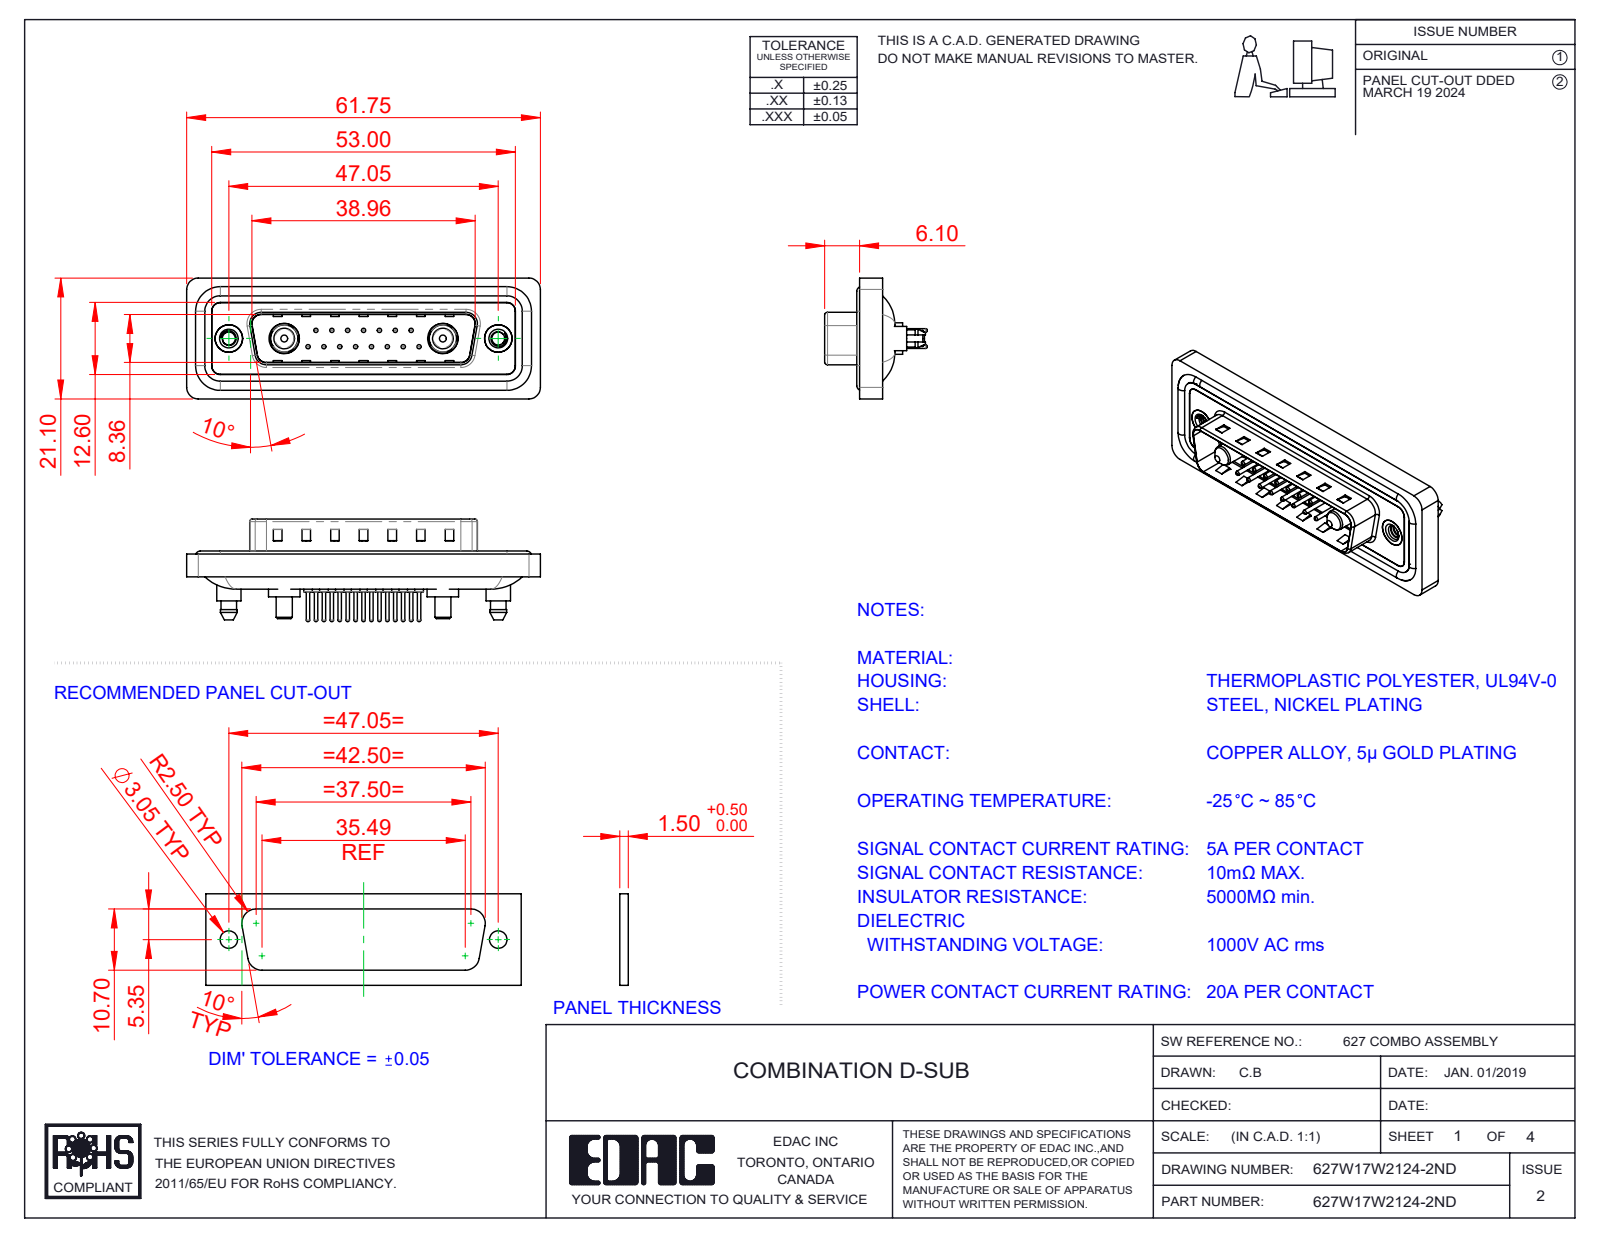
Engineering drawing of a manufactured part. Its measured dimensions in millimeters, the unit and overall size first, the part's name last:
Units: millimetres
Overall size (bounding box): 61.75 × 21.1 × 17.9
Round holes (diameter × count): ⌀0.75 ×15, ⌀1.6 ×15, ⌀2 ×15, ⌀2.26 ×2, ⌀4 ×2, ⌀4.8 ×2, ⌀4.85 ×2, ⌀5 ×2, ⌀5.3 ×2
Round bosses / shafts (diameter × count): ⌀1.5 ×15, ⌀0.6 ×15, ⌀1.6 ×4, ⌀5.5 ×2, ⌀5.4 ×2, ⌀5.2 ×2, ⌀4.9 ×2, ⌀4.75 ×2
Partial cylindrical surfaces — rounded edges, fillets, slot ends (radius × count): R1.5 ×24, R2 ×18, R1.6 ×10, R0.5 ×8, R0.25 ×4, R0.6 ×4, R0.65 ×4, R0.9 ×4
Main face-to-face distances: 0.4, 1.5, 1.1, 1.6, 0.5, 3.1, 2.9, 0.82, 9.58, 4.1
Hole centre spacings: 3.16, 2.77, 5.54, 8.31, 5.04, 7.49, 11.08, 5.03
Volume: 7 401 mm³ · Surface area: 12 250 mm²
Bodies: 26 solids, 1174 faces (350 planar, 476 cylindrical, 348 other)
Part name (STEP PRODUCT): 627Combo Contact Row 2_24; 627Combo Contact Row 1_24; 627Combo Shell Rear_25 Contacts; 627Combo Threaded Boardlock_D (+6 more)
STEP written by: SolidWorks 2023 (CONFIG_CONTROL_DESIGN)
